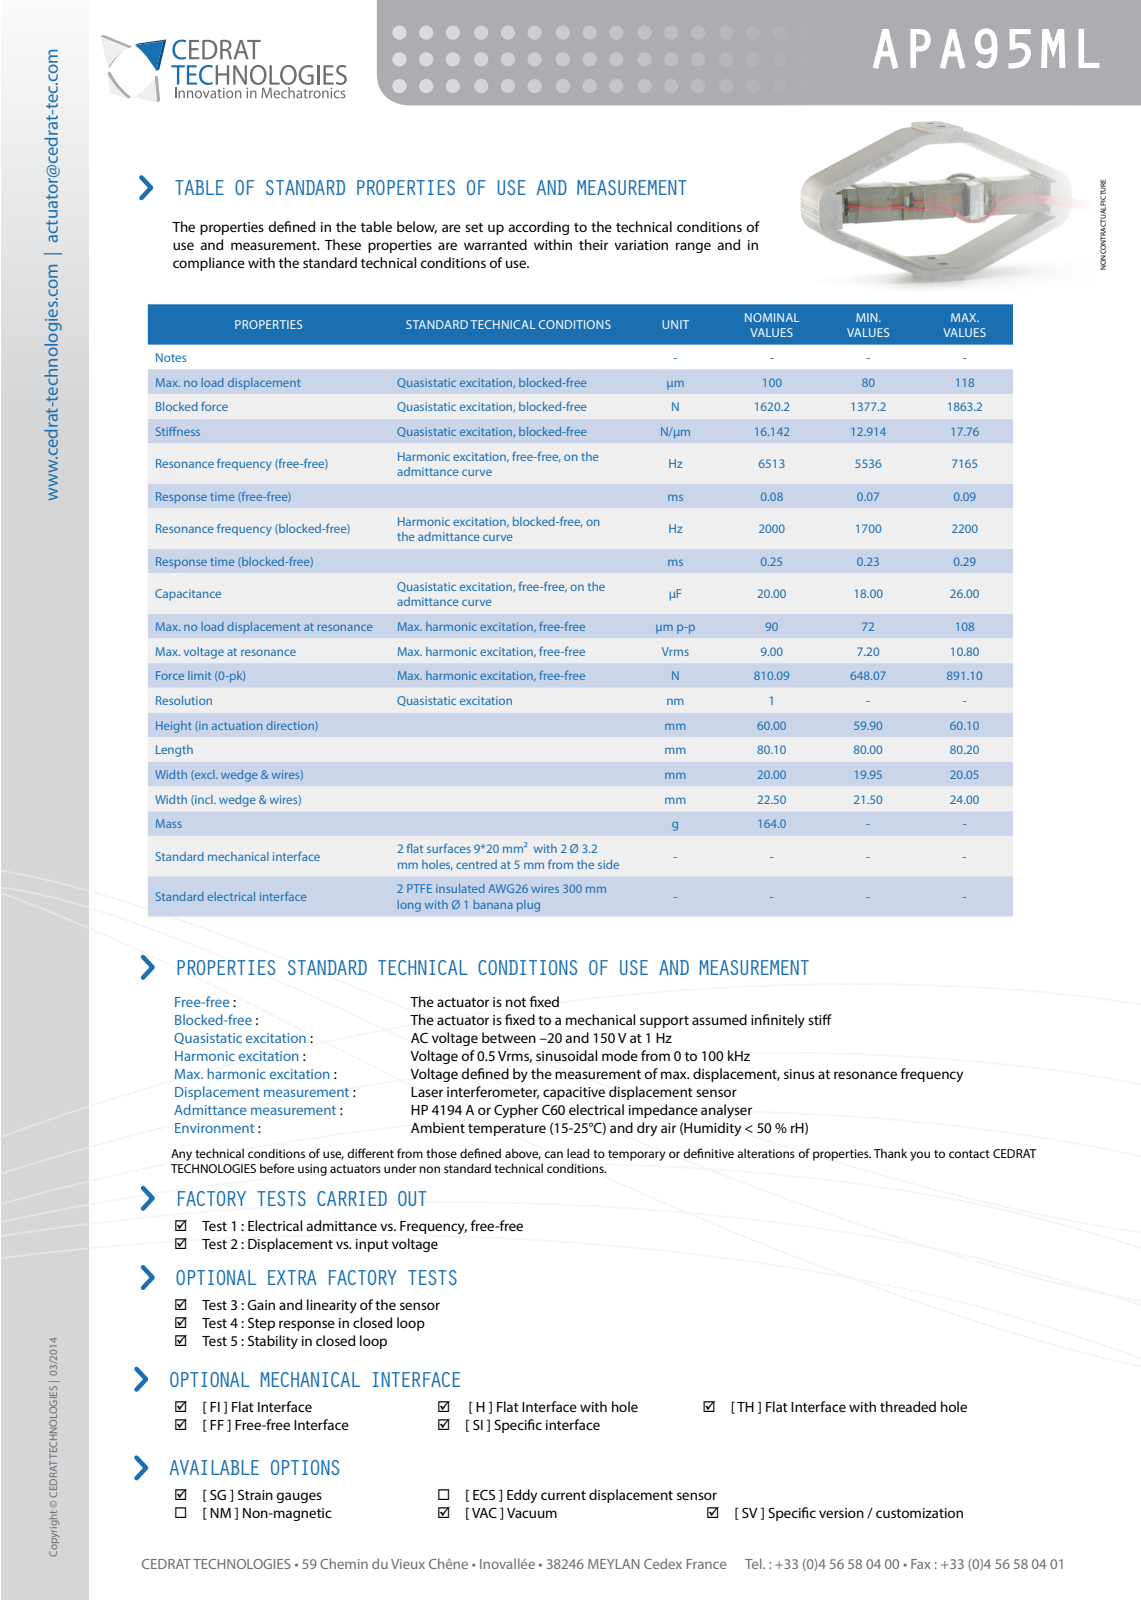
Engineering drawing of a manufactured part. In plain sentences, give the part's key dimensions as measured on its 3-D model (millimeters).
The part is named "000920_PAss APA95ML 02 +0.000". Its 3-D file was written by "SolidWorks 2010 (CONFIG_CONTROL_DESIGN)". It is 1 solid with 50 faces: 26 planar, 24 cylindrical and 0 other. Overall it measures 80.41 by 59.99 by 22.5 millimeters. Its volume is 44 907 cubic millimeters and its surface area 13 986 square millimeters. Round holes: 2 of diameter 3.2. Partial cylindrical surfaces (rounded edges, fillets, slot ends): 4 of radius 0.5, 4 of radius 0.8, 4 of radius 4, 4 of radius 8.29. The main face-to-face distances are 3.2, 51.04, 20, 22.5, 54.24, 47.84, 1.25, 21.25, 15.01, 35.01. The hole center spacings are 10.
